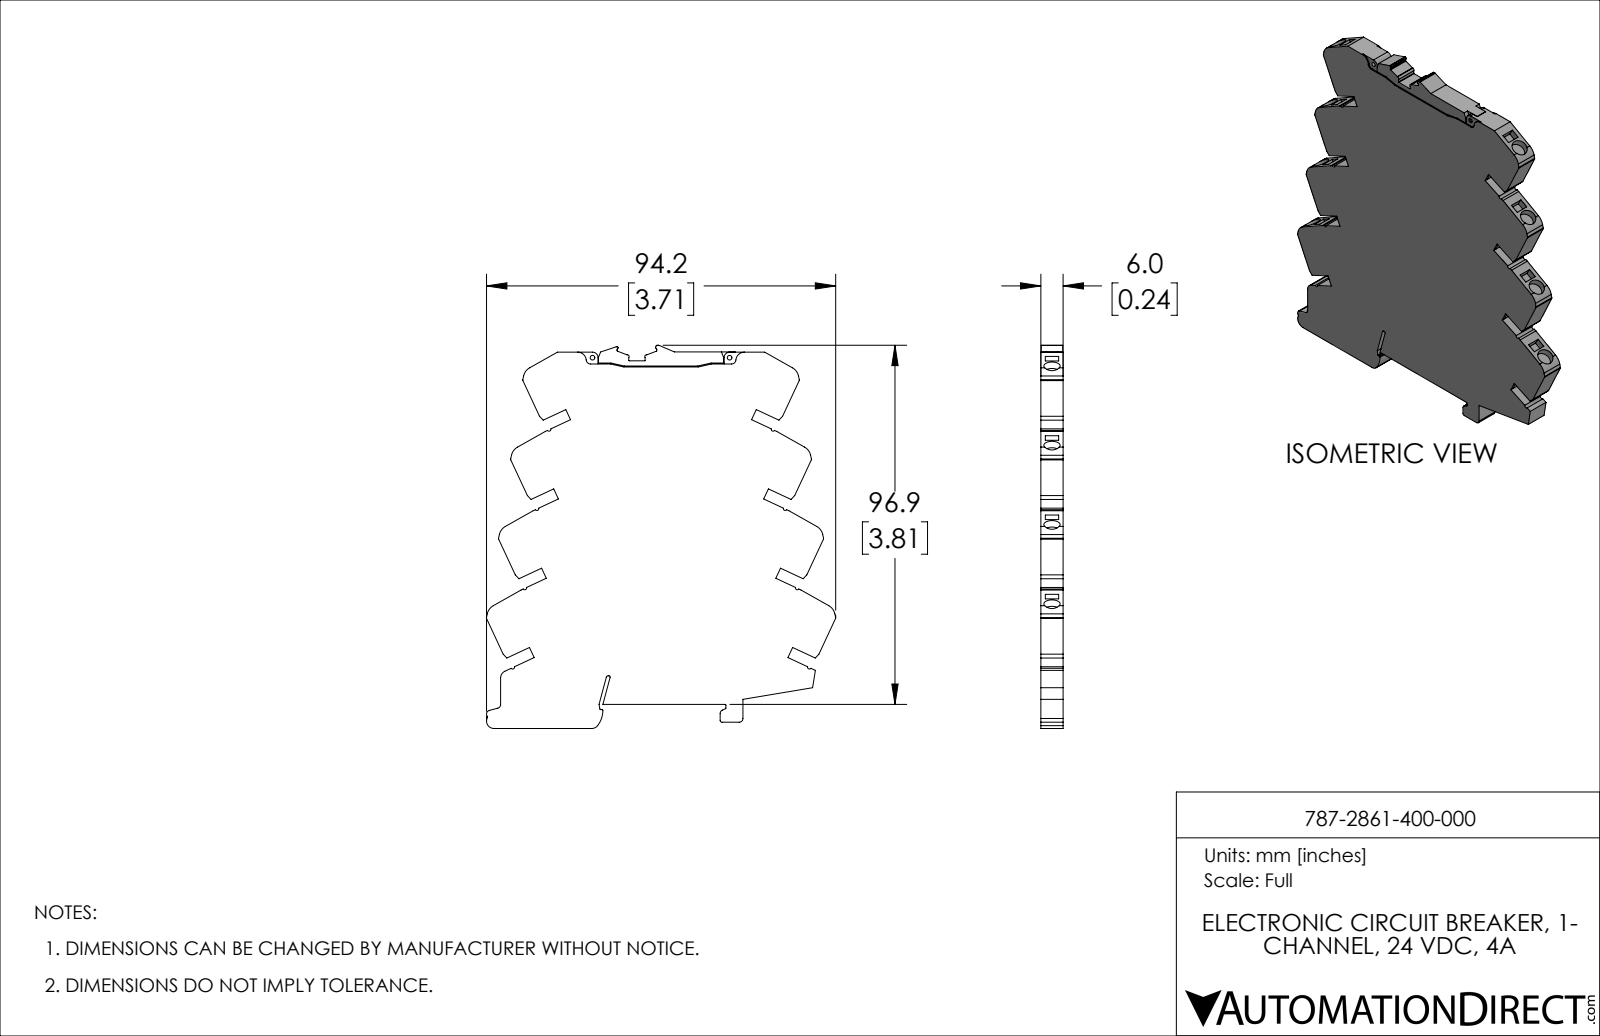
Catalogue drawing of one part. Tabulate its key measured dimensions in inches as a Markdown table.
| quantity | value |
| --- | --- |
| part name | 787-2861/400-000 |
| STEP written by | PARTsolutions (CONFIG_CONTROL_DESIGN) |
| units | inches |
| bodies | 1 solid, 294 faces (219 planar, 75 cylindrical, 0 other) |
| overall size | 4.069 × 3.711 × 0.236 |
| volume | 2.681 in³ |
| surface area | 29.86 in² |
| round holes (diameter × count) | 0.173 × 8, 0.049 × 2 |
| partial cylindrical surfaces (radius × count) | 0.02 × 12, 0.008 × 11, 0.016 × 8, 0.132 × 8, 0.039 × 4, 0.012 × 3, 0.079 × 3, 0.018 × 2 |
| main face-to-face distances | 0.236, 0.708, 0.67, 0.473, 0.232, 0.472, 0.118, 0.945, 1.417, 0.256 |
| hole center spacings | 0.526, 0.525, 1.051, 1.051, 1.052, 1.457, 1.576, 1.577 |
